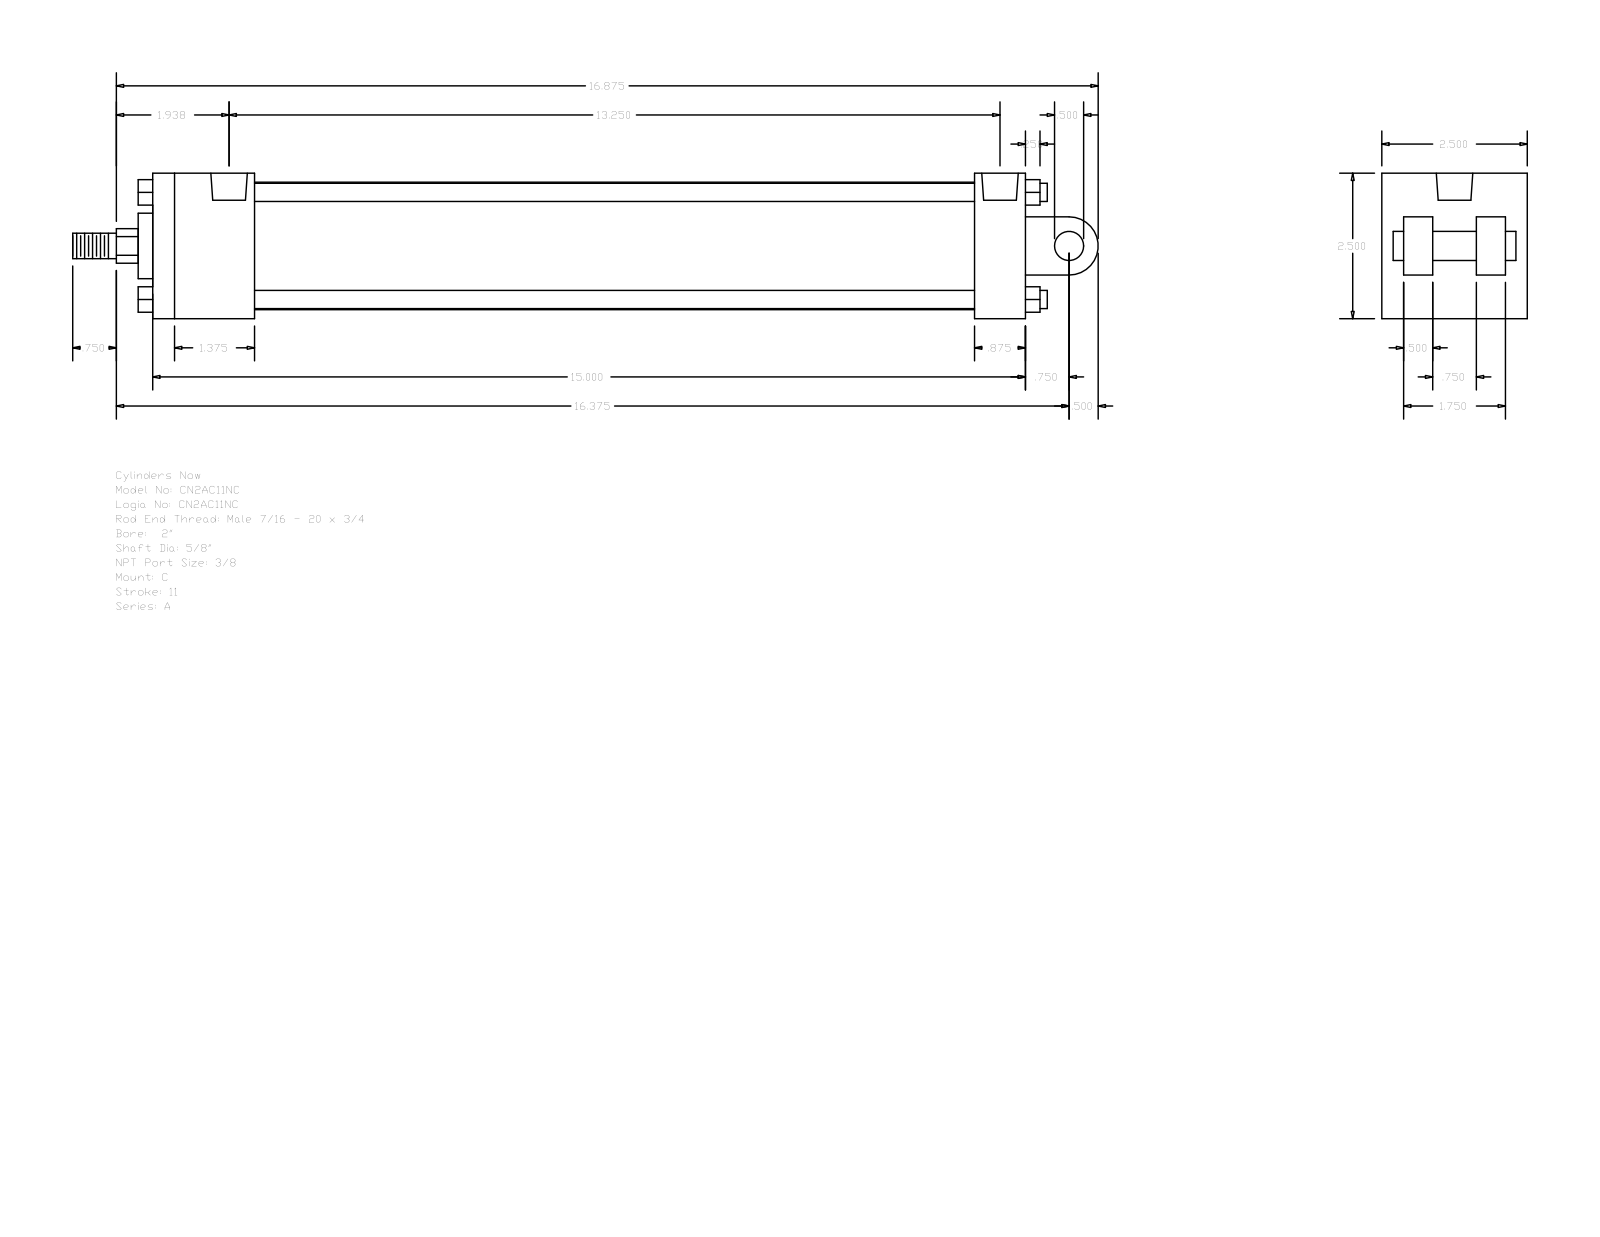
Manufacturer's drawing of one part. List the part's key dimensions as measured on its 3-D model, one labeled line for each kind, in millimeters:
Part name (STEP PRODUCT): A_C__0200_0.625
STEP written by: GSSL Pune (CONFIG_CONTROL_DESIGN)
Units: millimetres
Bodies: 0 solids, 135 faces (102 planar, 33 cylindrical, 0 other)
Overall size (bounding box): 447.68 × 63.5 × 63.5
Round holes (diameter × count): ⌀5.56 ×4, ⌀15.93 ×2
Round bosses / shafts (diameter × count): ⌀7.94 ×4, ⌀55.63 ×1, ⌀28.57 ×1, ⌀15.88 ×1, ⌀12.7 ×1, ⌀11.11 ×1
Partial cylindrical surfaces — rounded edges, fillets, slot ends (radius × count): R7.54 ×1, R12.7 ×1
Main face-to-face distances: 63.5, 381, 44.45, 9.52, 336.55, 358.77, 314.32, 22.23, 12.7, 6.35
Hole centre spacings: 328.6, 3.97, 3.98, 332.57, 332.58, 336.55
